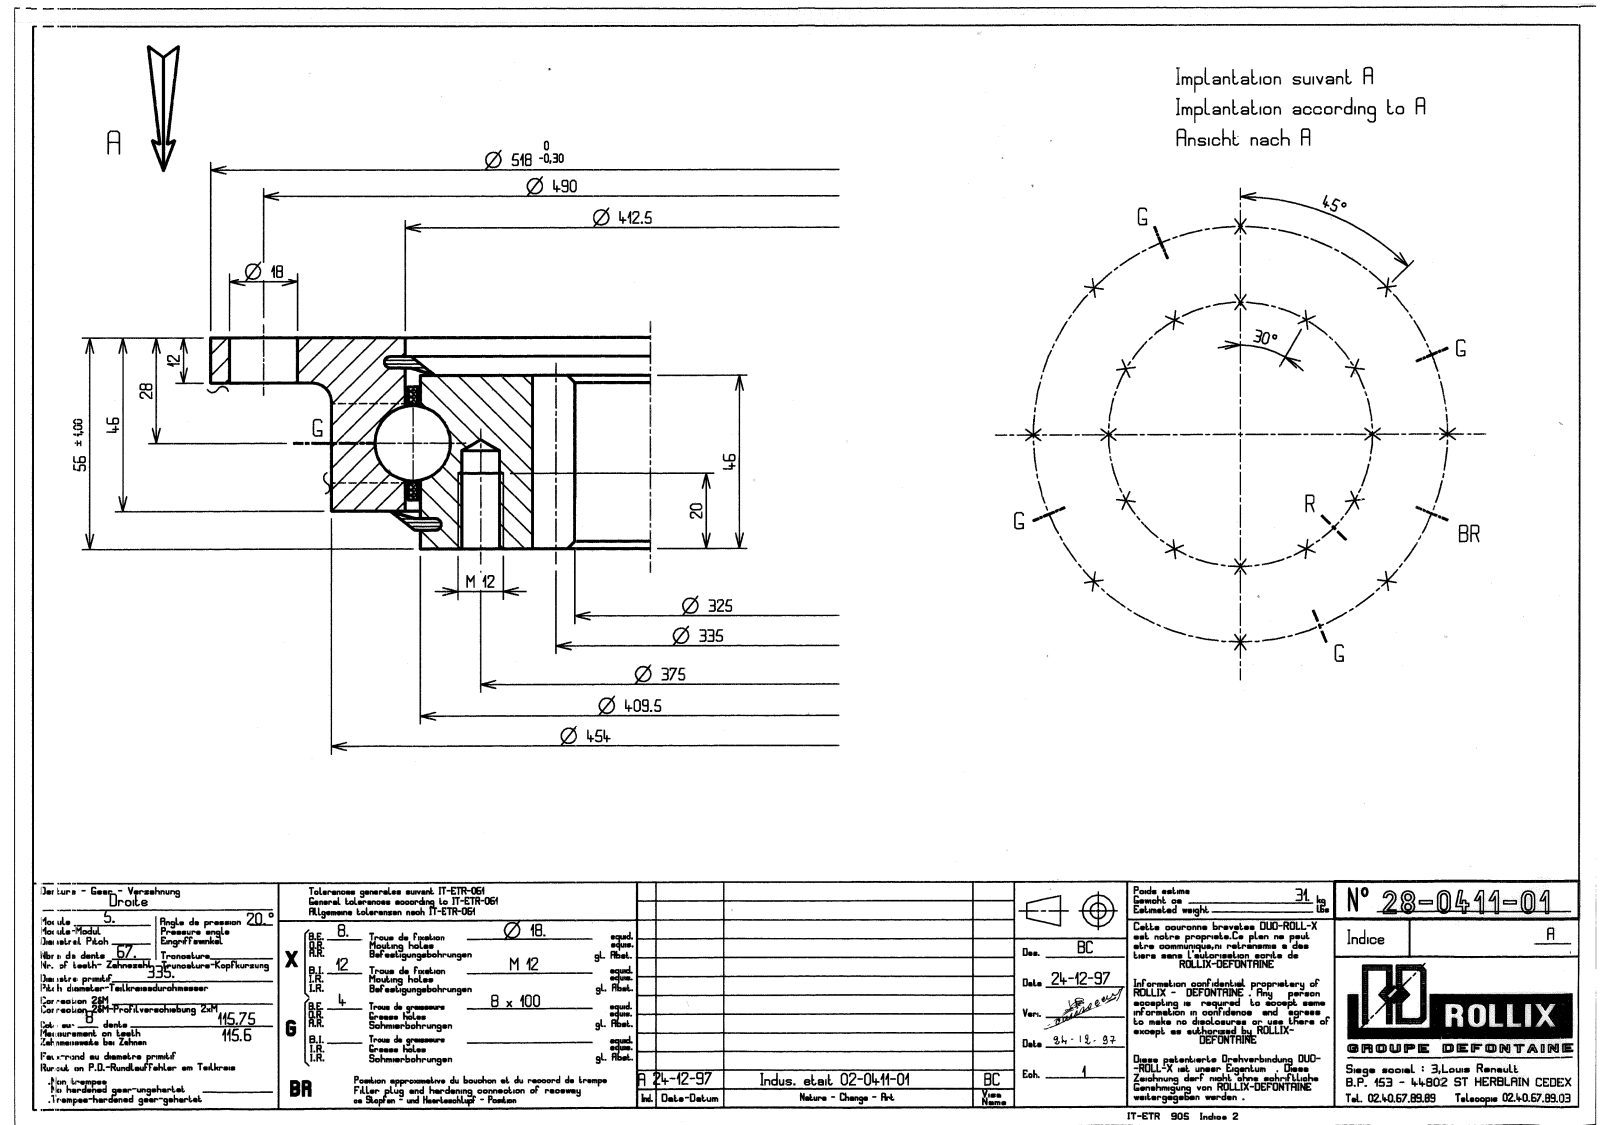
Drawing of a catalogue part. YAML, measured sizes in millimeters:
part_name: "22-0411-01"
step_written_by: "SolidWorks 2016 (CONFIG_CONTROL_DESIGN)"
units: millimeters
bodies: {solids: 9, faces: 623, planar: 187, cylindrical: 207, other: 229}
overall_size: [518, 518, 56]
volume: 3419000
surface_area: 645203
round_holes:
  - {diameter: 10.25, count: 12}
  - {diameter: 18, count: 8}
  - {diameter: 7, count: 4}
  - {diameter: 415.5, count: 1}
round_bosses_or_shafts:
  - {diameter: 8, count: 4}
  - {diameter: 518, count: 1}
  - {diameter: 454, count: 1}
  - {diameter: 406.5, count: 1}
partial_cylinders:
  - {radius: 162.5, count: 1}
  - {radius: 173.75, count: 1}
face_to_face_distances: [10, 46, 56, 44, 2, 12, 34, 36, 8.05, 47.95]
hole_center_spacings: [187.5, 97.06, 265.17, 324.76, 362.22, 80.23, 124.96, 173.83]
